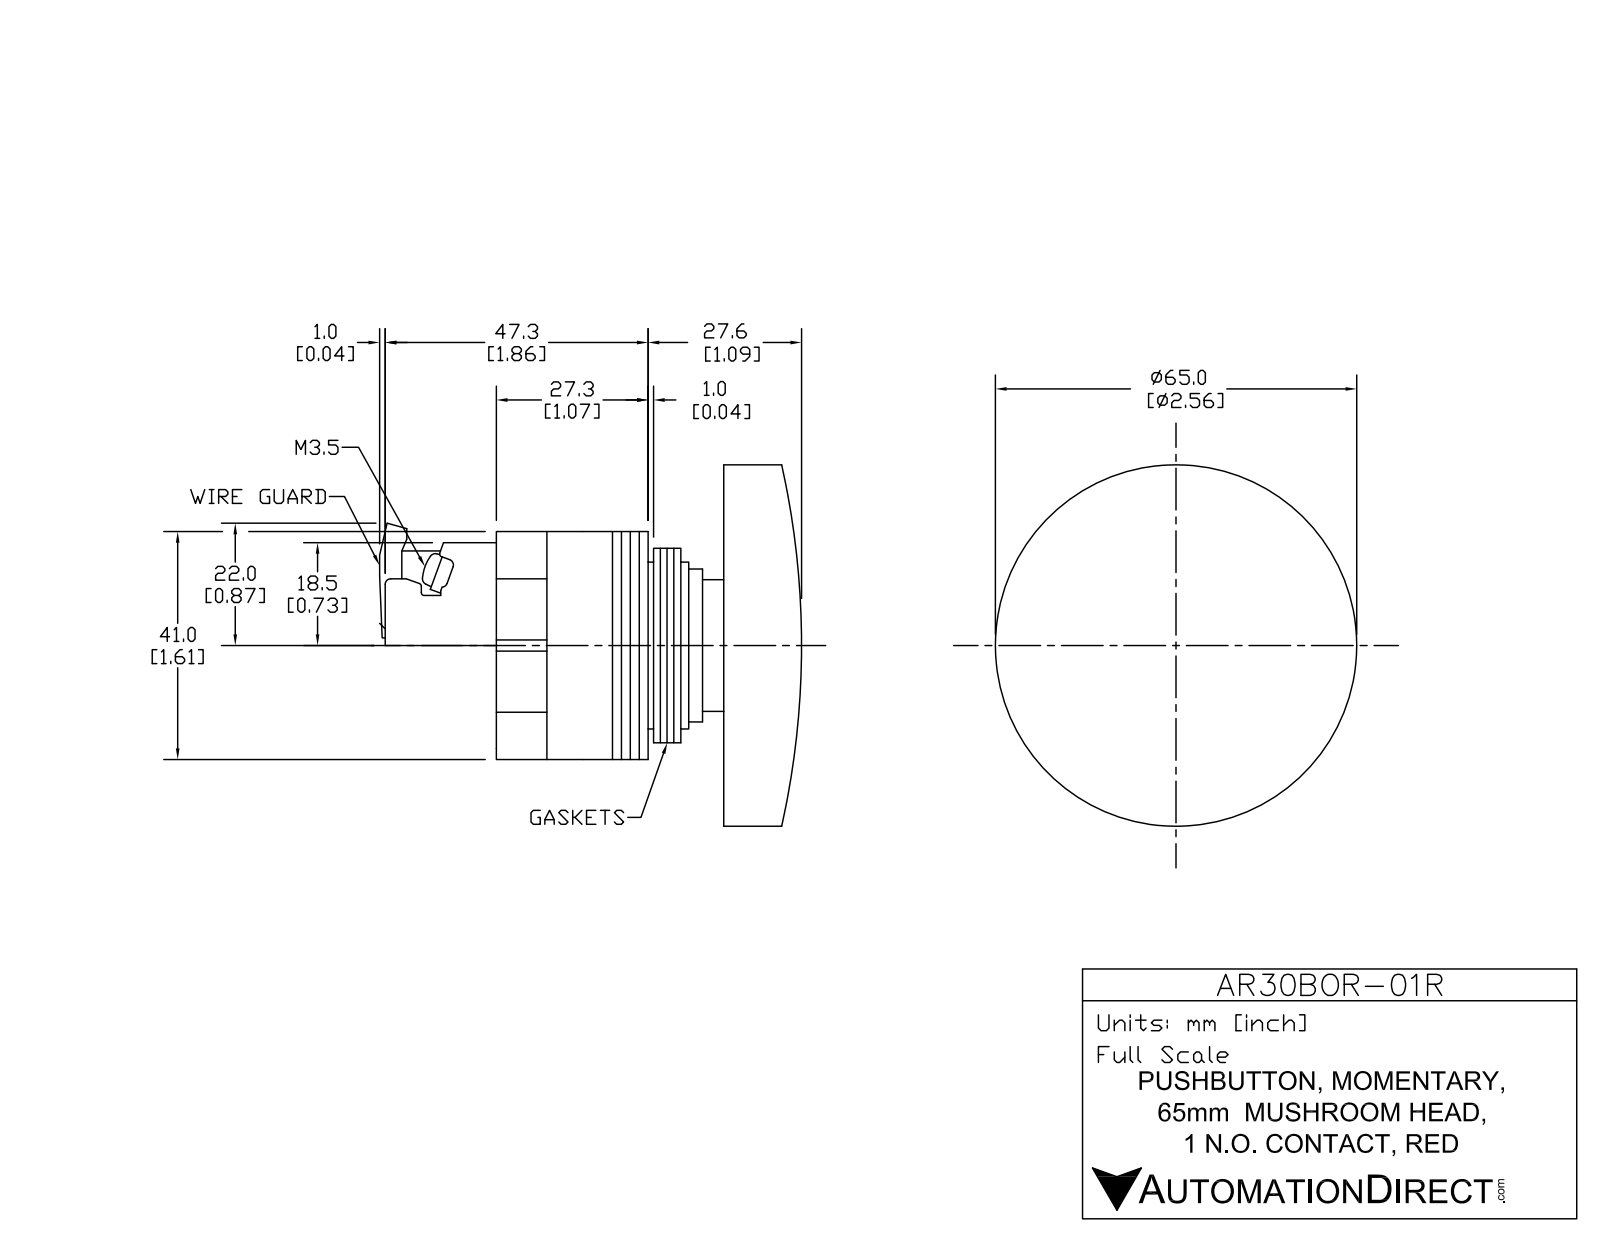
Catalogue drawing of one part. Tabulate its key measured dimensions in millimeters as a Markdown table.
| quantity | value |
| --- | --- |
| part name | AR30B0R-01R |
| STEP written by | SolidWorks 2017 (AUTOMOTIVE_DESIGN) |
| units | millimeters |
| bodies | 14 solids, 246 faces (140 planar, 92 cylindrical, 14 other) |
| overall size | 76 × 65 × 65 |
| volume | 74 048 mm³ |
| surface area | 37 582 mm² |
| round holes (diameter × count) | 3 × 4, 24 × 1, 30 × 1, 60 × 1 |
| round bosses / shafts (diameter × count) | 5 × 2, 65 × 1, 40 × 1, 35 × 1, 29.8 × 1 |
| partial cylindrical surfaces (radius × count) | 5 × 10, 0.5 × 8, 1.75 × 4, 3 × 4, 2 × 2 |
| main face-to-face distances | 1.6, 3.2, 16, 21, 5, 41, 4.8, 15.99, 5.01, 25 |
| hole center spacings | 21.92, 31, 43.84 |
